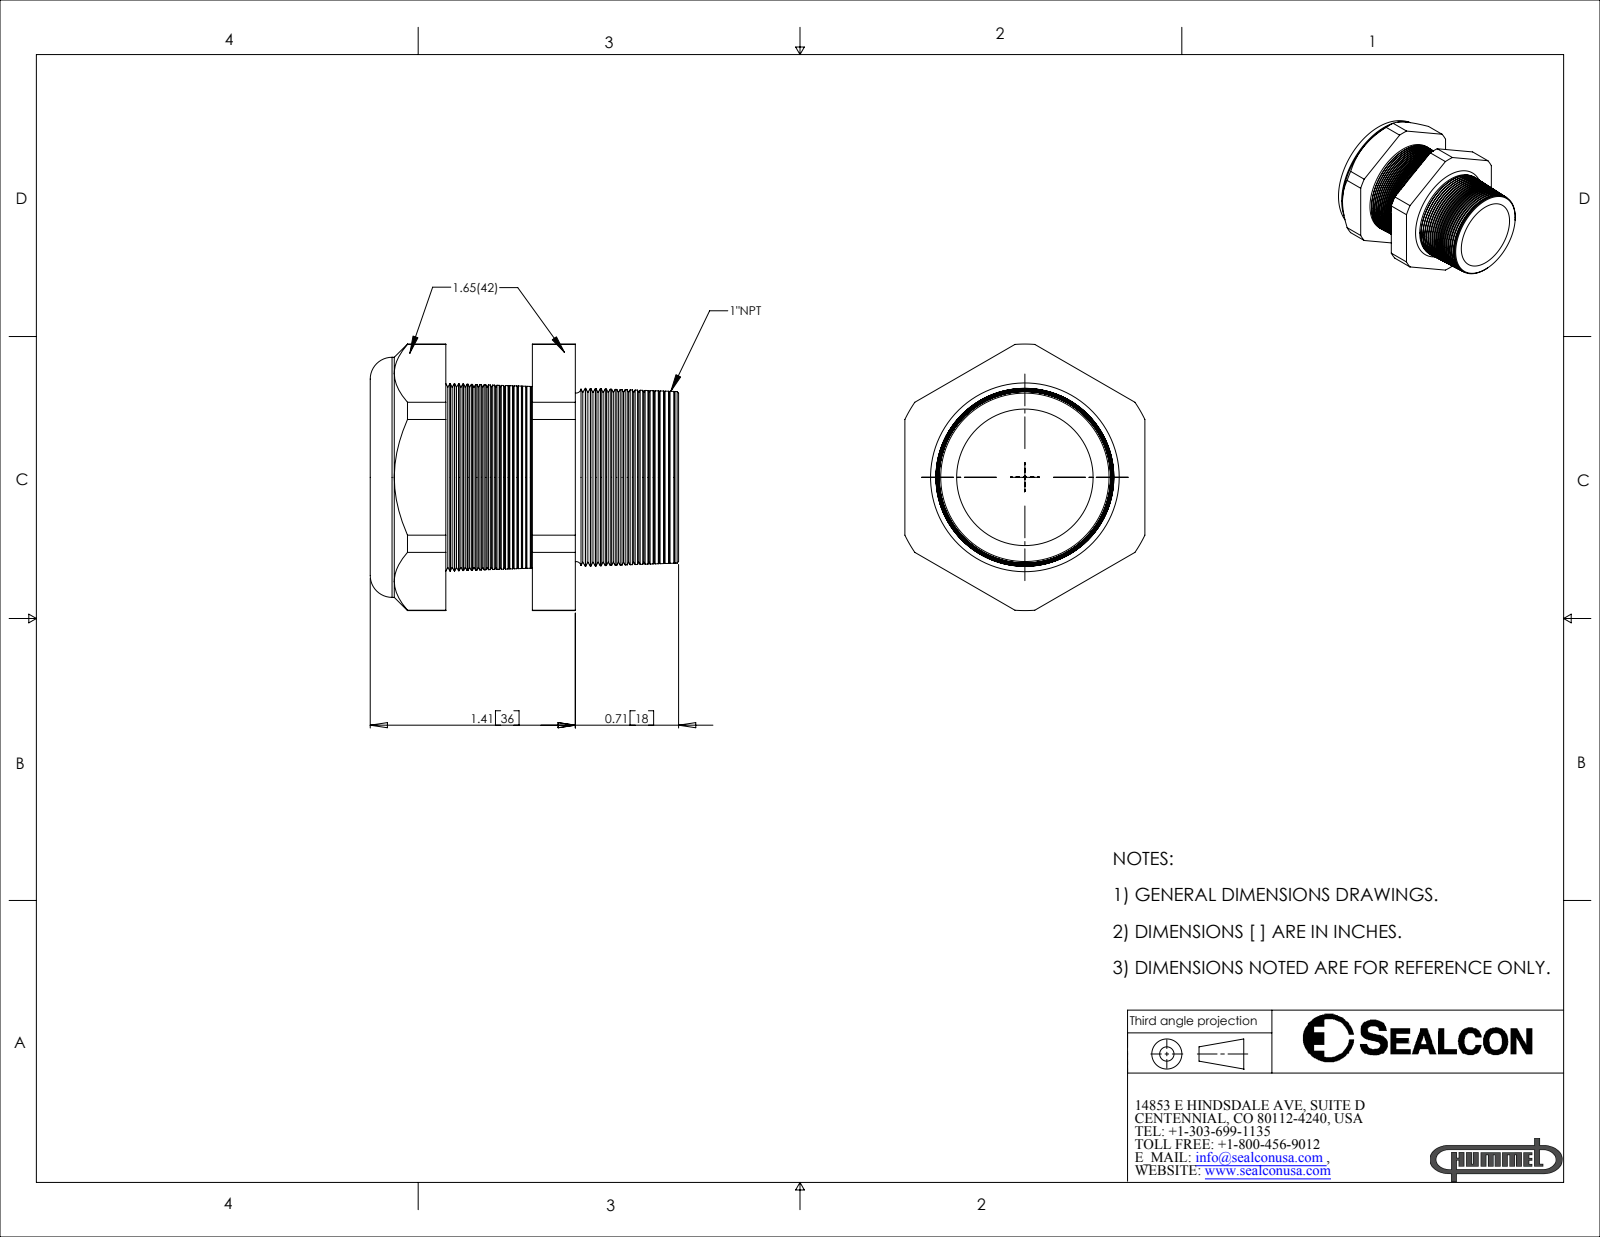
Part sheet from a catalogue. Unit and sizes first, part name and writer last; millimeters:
Units: millimetres
Overall size (bounding box): 53.8 × 46.5 × 41.9
Round holes (diameter × count): ⌀24.4 ×1, ⌀24.9 ×1
Round bosses / shafts (diameter × count): ⌀41.9 ×1
Partial cylindrical surfaces — rounded edges, fillets, slot ends (radius × count): R23.3 ×1
Main face-to-face distances: 14.1, 21.6, 7.5, 41.9, 0.5, 14.6, 22.1, 12.2, 12.7, 26.8
Volume: 35 710 mm³ · Surface area: 17 420 mm²
Bodies: 2 solids, 290 faces (20 planar, 20 cylindrical, 250 other)
Part name (STEP PRODUCT): CD29NP-GY
STEP written by: SolidWorks 2007 (CONFIG_CONTROL_DESIGN)
